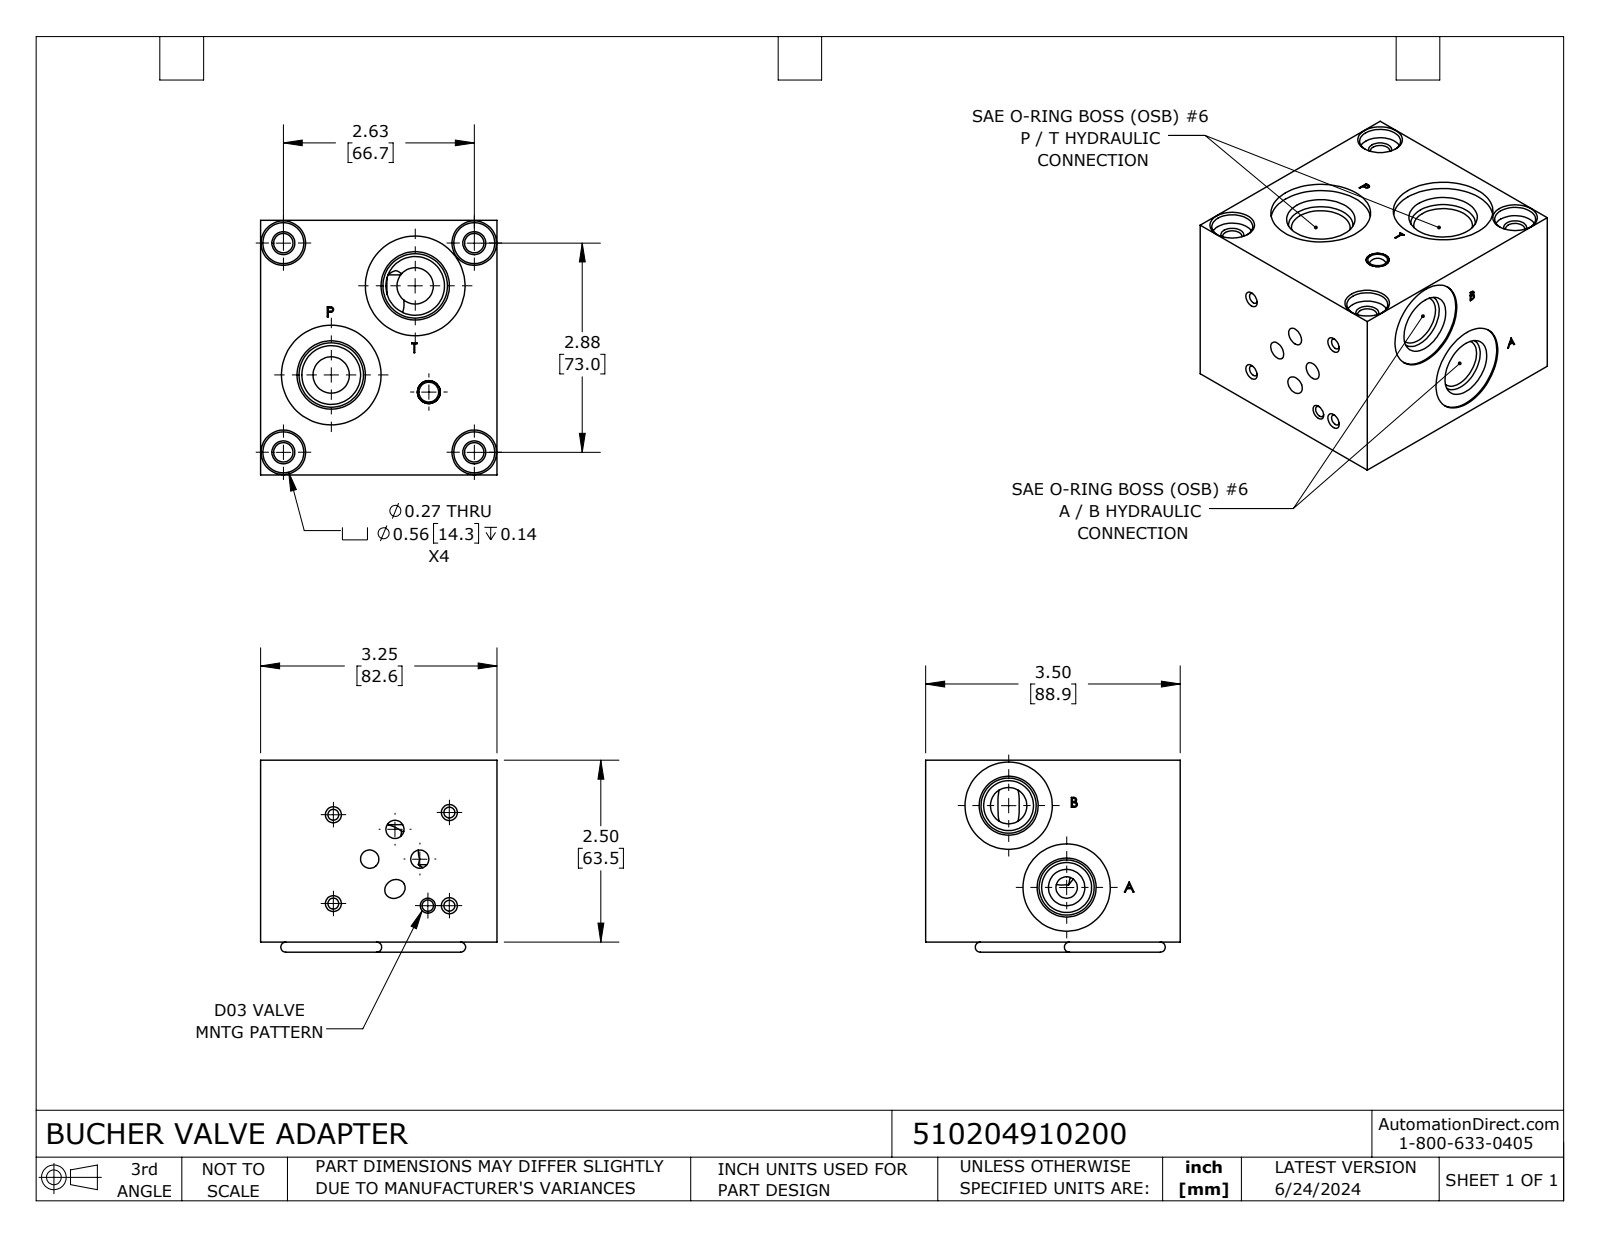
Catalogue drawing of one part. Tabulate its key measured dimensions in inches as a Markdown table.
| quantity | value |
| --- | --- |
| part name | 510204910200 |
| STEP written by | SolidWorks 2023 (CONFIG_CONTROL_DESIGN) |
| units | inches |
| bodies | 4 solids, 566 faces (253 planar, 70 cylindrical, 243 other) |
| overall size | 3.5 × 3.25 × 2.639 |
| volume | 24.9 in³ |
| surface area | 89.42 in² |
| round holes (diameter × count) | 0.15 × 4, 0.25 × 4, 0.266 × 4, 0.5 × 4, 0.563 × 4, 0.686 × 2, 0.807 × 2, 1.2 × 2, 1.37 × 2, 0.156 × 1, 0.271 × 1, 0.291 × 1 |
| round bosses / shafts (diameter × count) | 0.315 × 1 |
| main face-to-face distances | 3.5, 2.5, 3.25, 0.105, 2.395, 3.23, 0.02, 0.165, 0.06, 2.335 |
| hole center spacings | 1.595, 2.625, 2.875, 3.893, 0.296, 0.533, 0.65, 0.757 |
